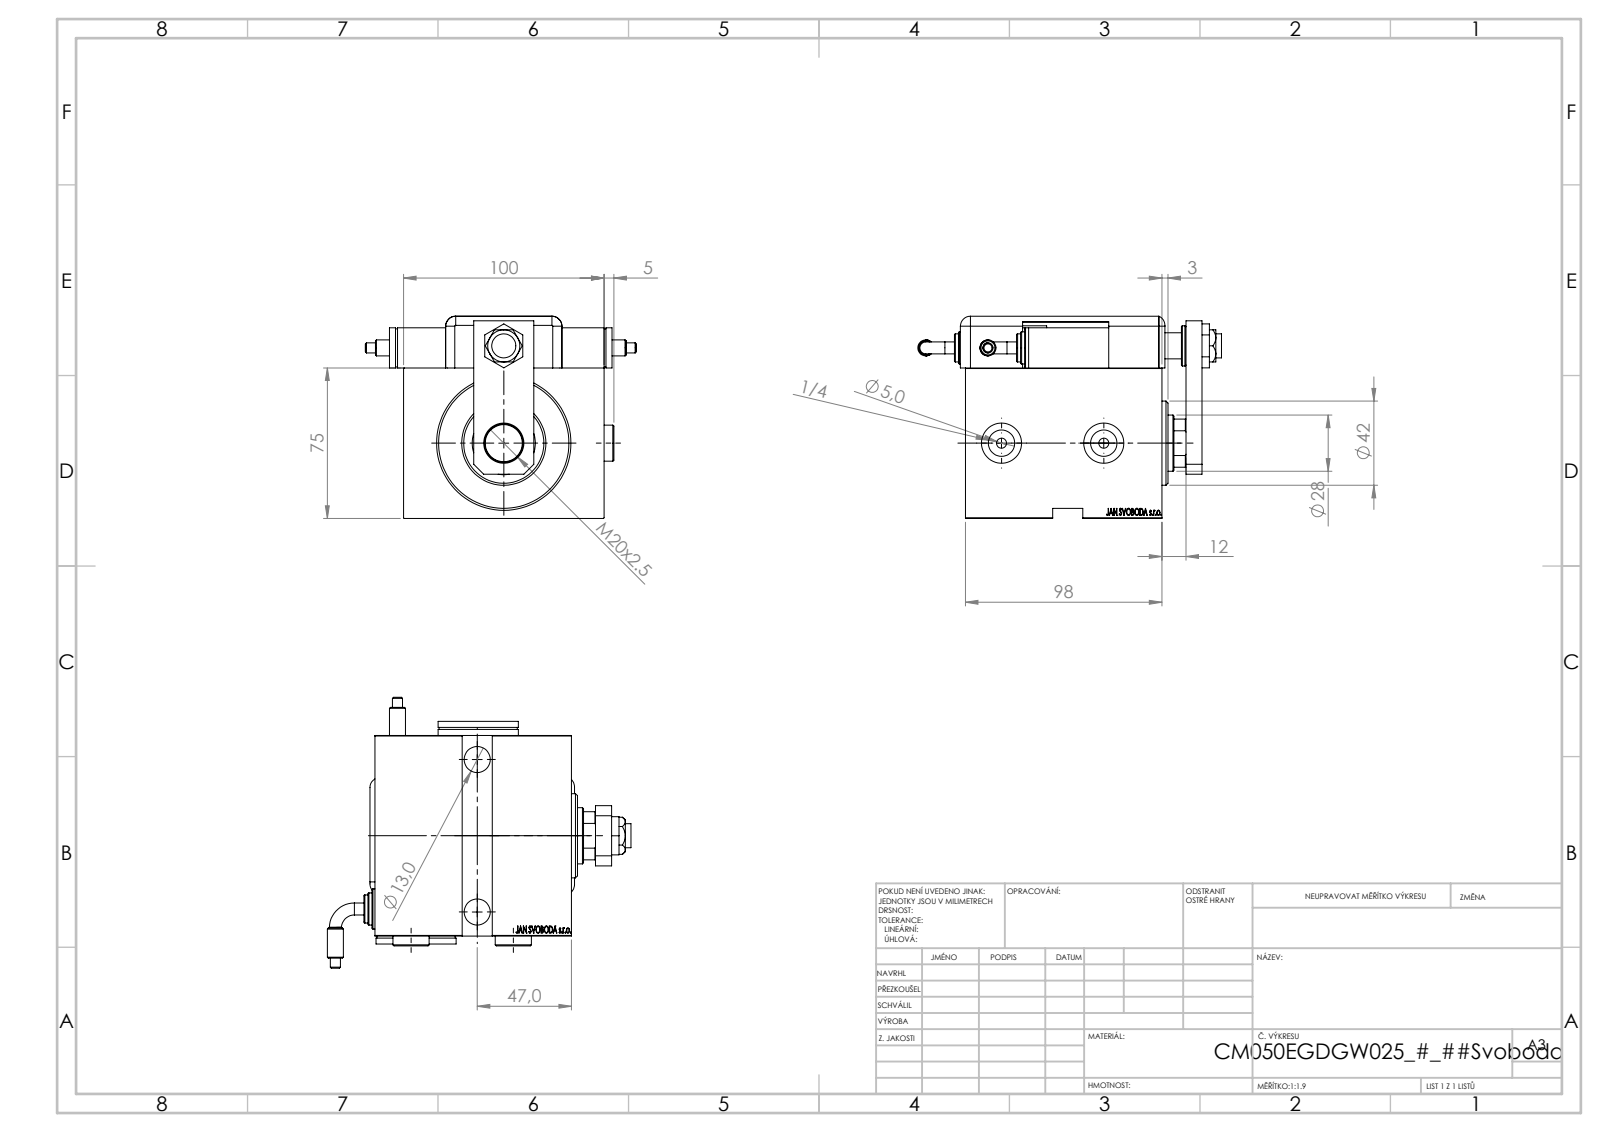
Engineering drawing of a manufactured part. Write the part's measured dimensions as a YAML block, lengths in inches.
part_name: "V450CM_E_VCP; NUT_D13; SWITCH_Q_FRONT_BACK; SWITCH DIM A_G (+7 more)"
step_written_by: "SolidWorks 2019 (CONFIG_CONTROL_DESIGN)"
units: inches
bodies: {solids: 15, faces: 1314, planar: 654, cylindrical: 123, other: 537}
overall_size: [5.963, 5.315, 3.969]
volume: 49.78
surface_area: 242.7
round_holes:
  - {diameter: 0.512, count: 3}
  - {diameter: 0.787, count: 3}
  - {diameter: 0.157, count: 2}
  - {diameter: 0.197, count: 2}
  - {diameter: 0.315, count: 2}
  - {diameter: 0.518, count: 2}
  - {diameter: 0.748, count: 2}
  - {diameter: 0.472, count: 1}
  - {diameter: 0.551, count: 1}
  - {diameter: 0.728, count: 1}
  - {diameter: 1.102, count: 1}
  - {diameter: 1.24, count: 1}
round_bosses_or_shafts:
  - {diameter: 0.787, count: 3}
  - {diameter: 0.709, count: 2}
  - {diameter: 0.63, count: 2}
  - {diameter: 0.551, count: 2}
  - {diameter: 0.315, count: 2}
  - {diameter: 0.236, count: 2}
  - {diameter: 0.198, count: 2}
  - {diameter: 2.047, count: 1}
partial_cylinders:
  - {radius: 0.197, count: 9}
  - {radius: 0.394, count: 1}
  - {radius: 0.531, count: 1}
face_to_face_distances: [0.118, 2.953, 3.858, 3.937, 0.551, 0.787, 3.307, 3.11, 3.969, 1.016]
hole_center_spacings: [1.858, 2.41, 0.787, 1.909, 2.008, 2.992]
